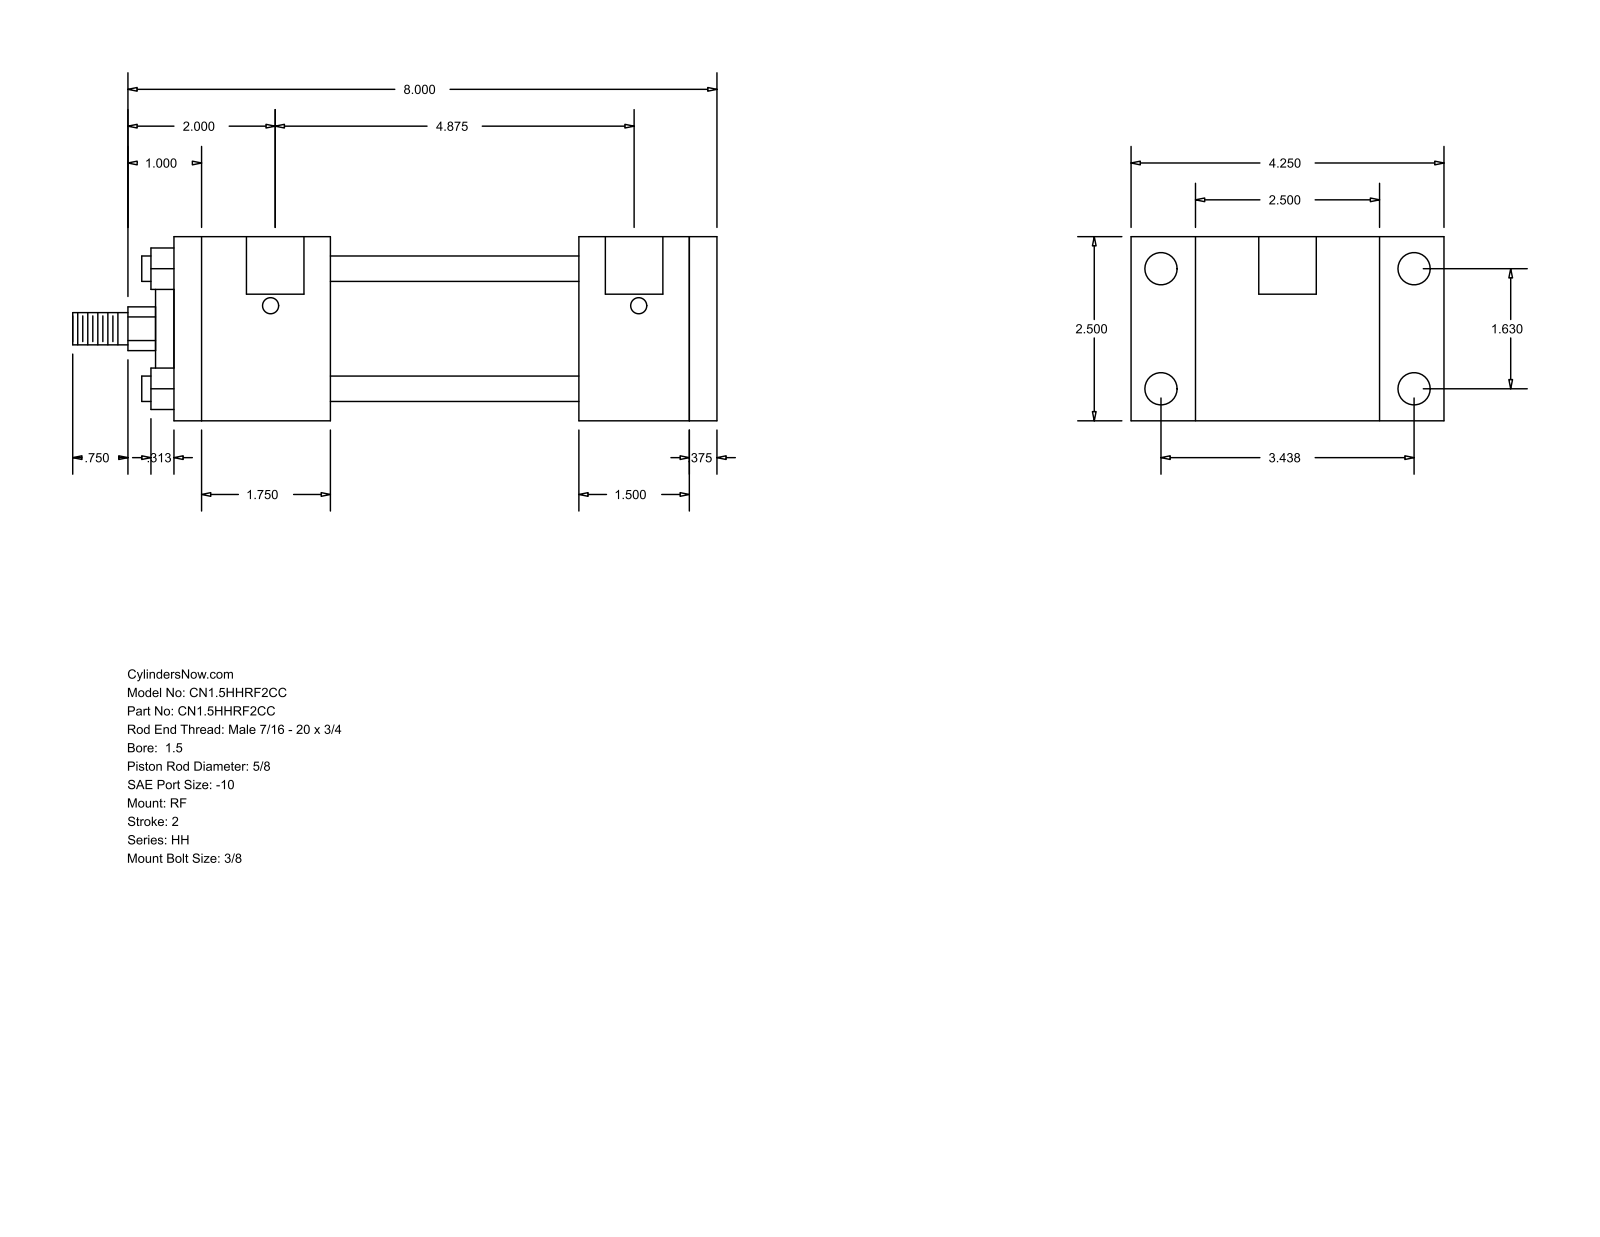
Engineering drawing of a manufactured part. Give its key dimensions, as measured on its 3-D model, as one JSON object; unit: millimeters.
{"part_name": "HH_RF__0150_0.625", "step_written_by": "GSSL Pune (CONFIG_CONTROL_DESIGN)", "units": "millimeters", "bodies": {"solids": 0, "faces": 92, "planar": 64, "cylindrical": 28, "other": 0}, "overall_size": [222.25, 107.95, 63.5], "round_holes": [[5.56, 4], [11.13, 4], [19.84, 2]], "round_bosses_or_shafts": [[8.76, 4], [44.45, 1], [28.57, 1], [15.88, 1], [11.11, 1]], "partial_cylinders_radius": [[7.54, 1]], "face_to_face_distances": [63.5, 187.32, 177.8, 9.52, 47.63, 53.97, 139.69, 85.72, 123.83, 133.35], "hole_center_spacings": [1.59, 41.4, 87.32, 96.64, 125.41, 127, 123.82]}
